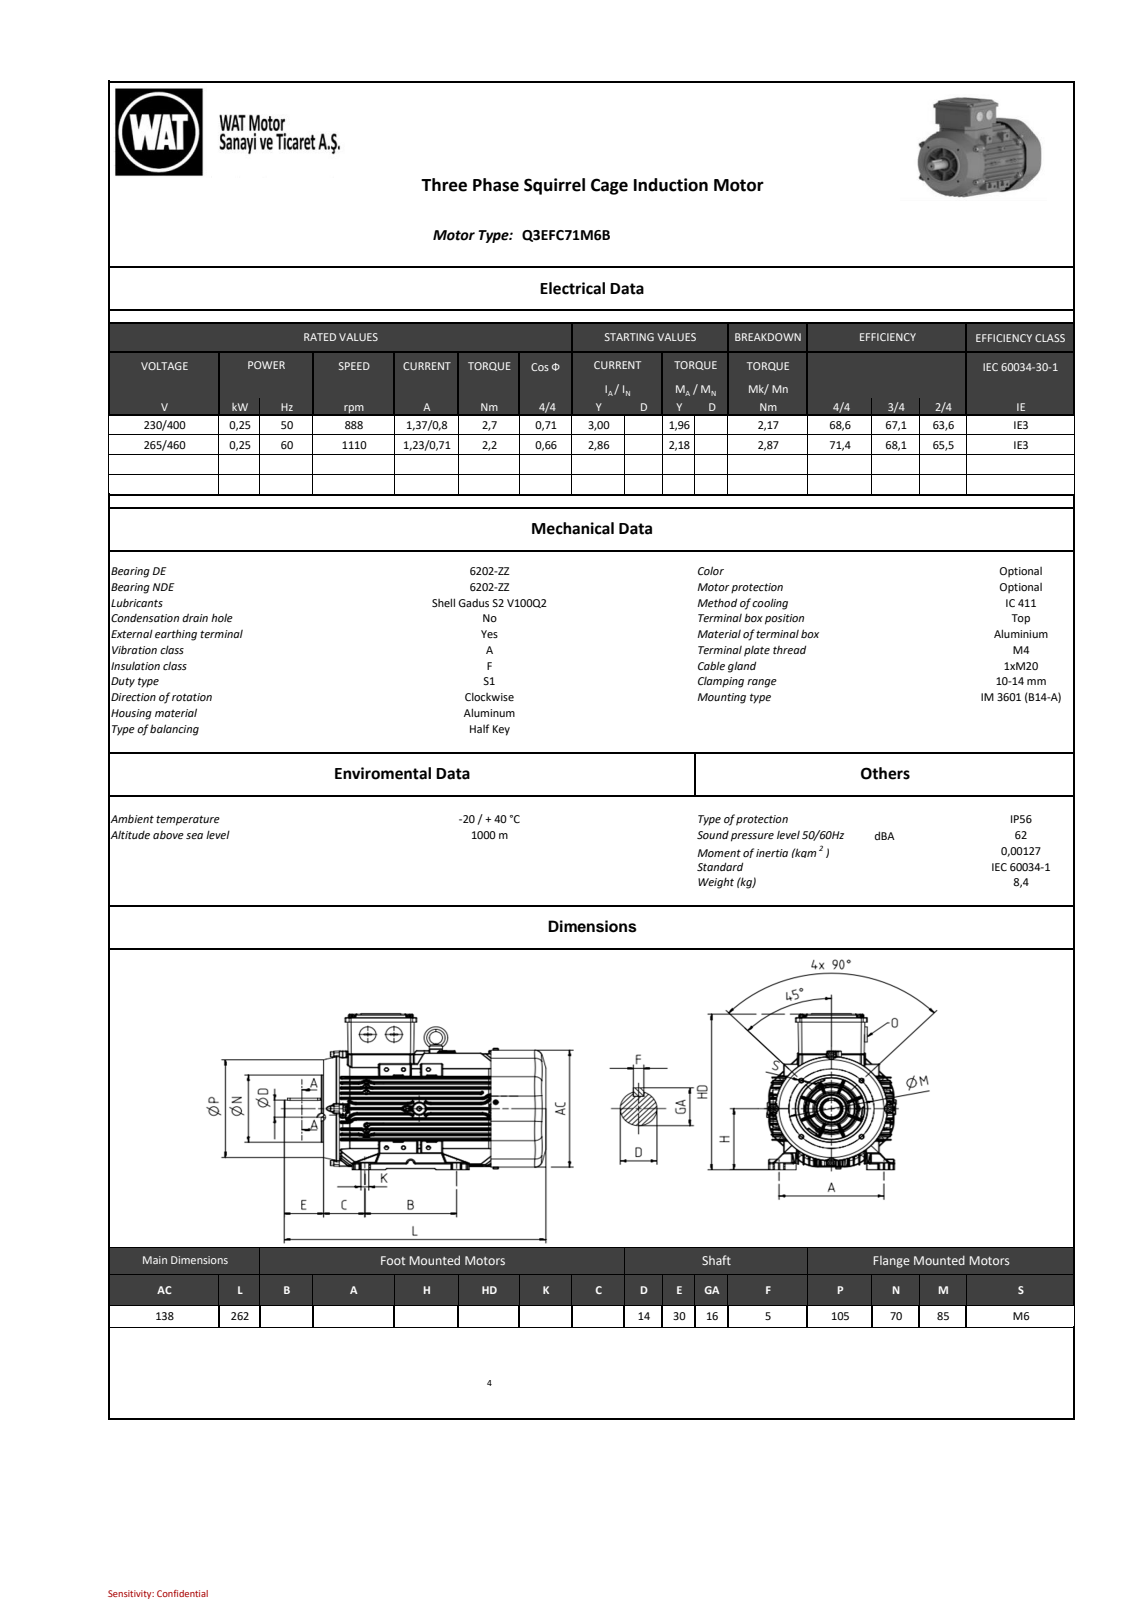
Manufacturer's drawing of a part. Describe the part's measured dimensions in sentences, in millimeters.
The part is named "001_objects". Its 3-D file was written by "SIEMENS PLM Software NX2206.8101 (AUTOMOTIVE_DESIGN)". It is 0 solids with 2797 faces: 1400 planar, 727 cylindrical and 670 other. Overall it measures 262 by 176.11 by 138 millimeters. Round holes: 8 of diameter 3.65, 7 of diameter 3, 6 of diameter 2.5, 5 of diameter 3.3, 5 of diameter 5, 4 of diameter 4, 4 of diameter 4.5, 4 of diameter 4.65, 4 of diameter 4.8, 3 of diameter 3.7, 2 of diameter 4.6, 1 of diameter 6. Round bosses or shafts: 8 of diameter 8, 8 of diameter 4, 4 of diameter 12, 4 of diameter 3.3, 1 of diameter 138, 1 of diameter 70, 1 of diameter 61, 1 of diameter 26. Partial cylindrical surfaces (rounded edges, fillets, slot ends): 111 of radius 1, 51 of radius 0.5, 36 of radius 1.2, 24 of radius 1.5, 19 of radius 5, 17 of radius 4, 16 of radius 3.25, 16 of radius 10. The main face-to-face distances are 3, 2, 194.5, 1, 83, 5, 35, 197.5, 4, 32. The hole center spacings are 61.39, 87.43, 55, 36.59, 67.18, 67.2, 60, 8.61.
